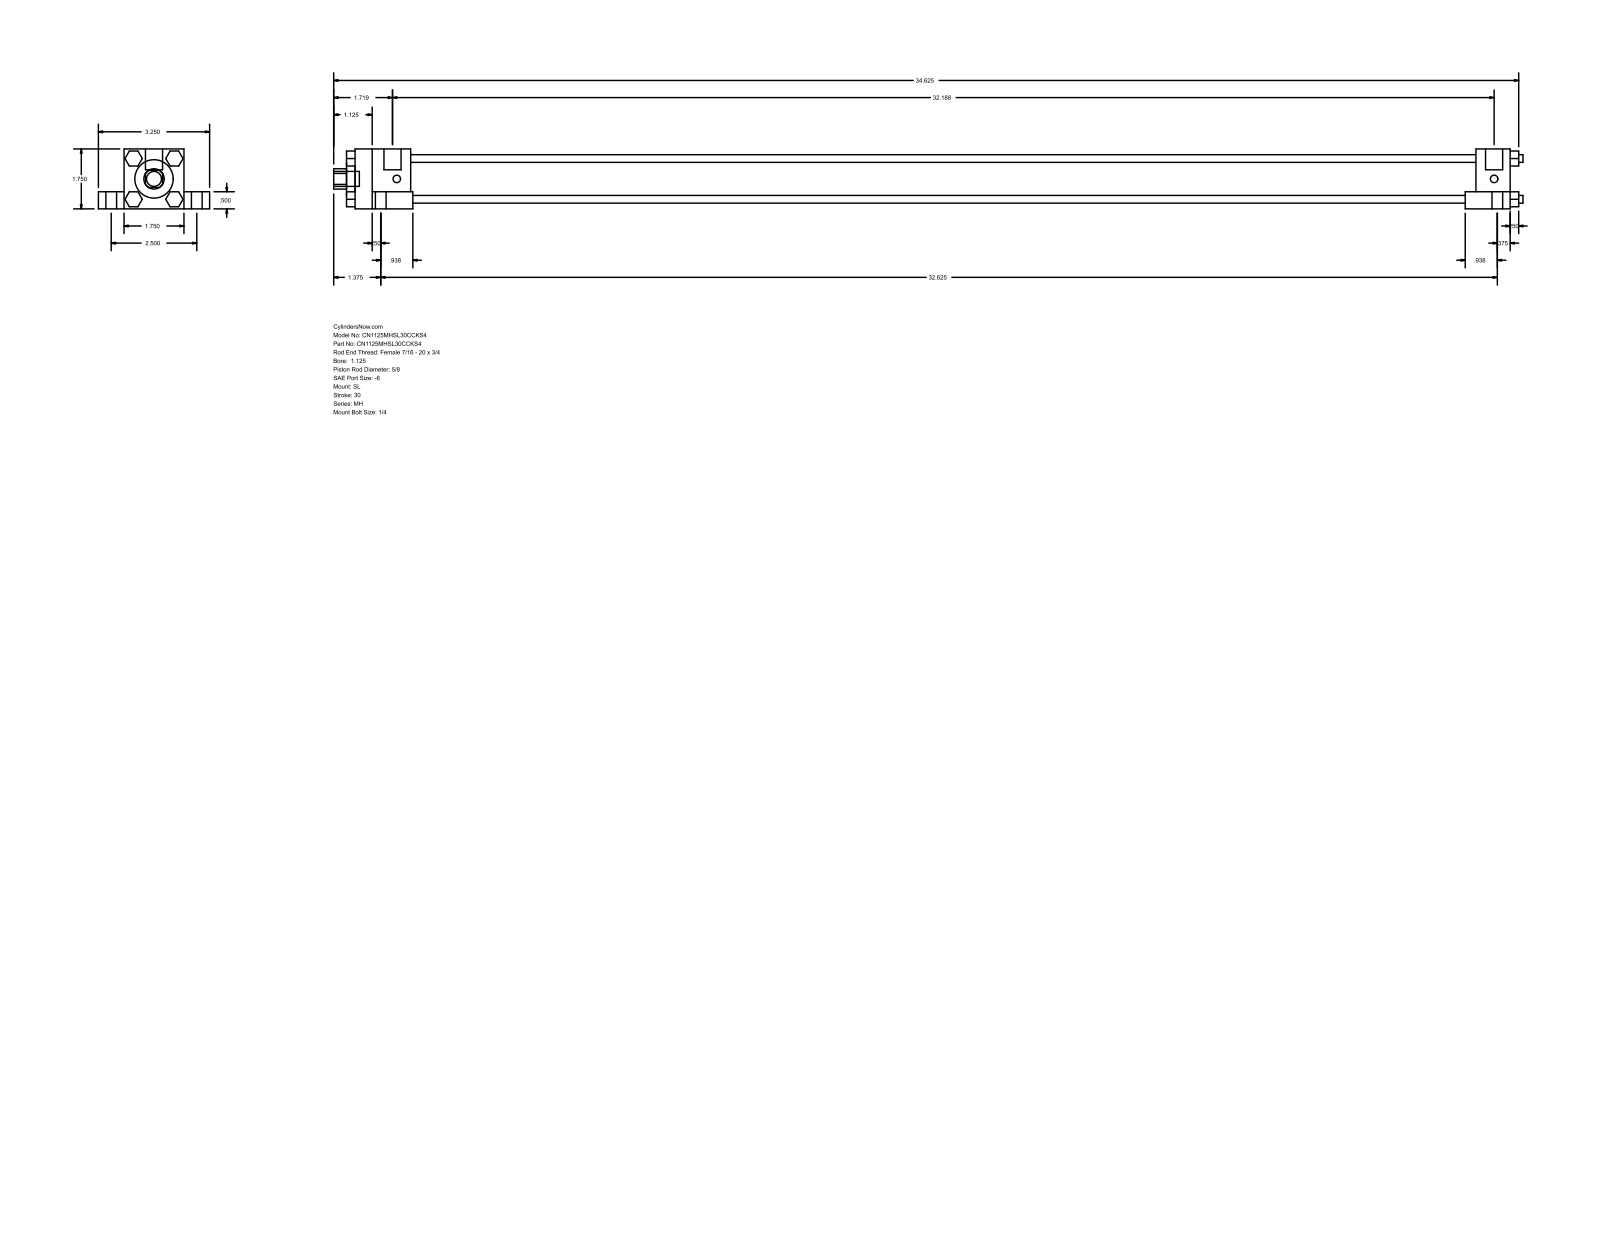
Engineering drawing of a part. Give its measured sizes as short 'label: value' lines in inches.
name: MH_SL__0112_0.625
written by: GSSL Pune (CONFIG_CONTROL_DESIGN)
unit: in
bodies: 0 solids, 150 faces (114 planar, 36 cylindrical, 0 other)
size: 34.75 × 3.25 × 1.75
holes: 1× ⌀0.625, 1× ⌀1.125, 1× ⌀1.375
bosses: 4× ⌀0.563, 4× ⌀0.313, 4× ⌀0.225, 4× ⌀0.219, 2× ⌀0.5, 1× ⌀0.437
rounds: 1× R0.297
face distances: 1.75, 0.75, 0.5, 1.25, 2.5, 0.437, 31.125, 32.125, 1, 1.625
